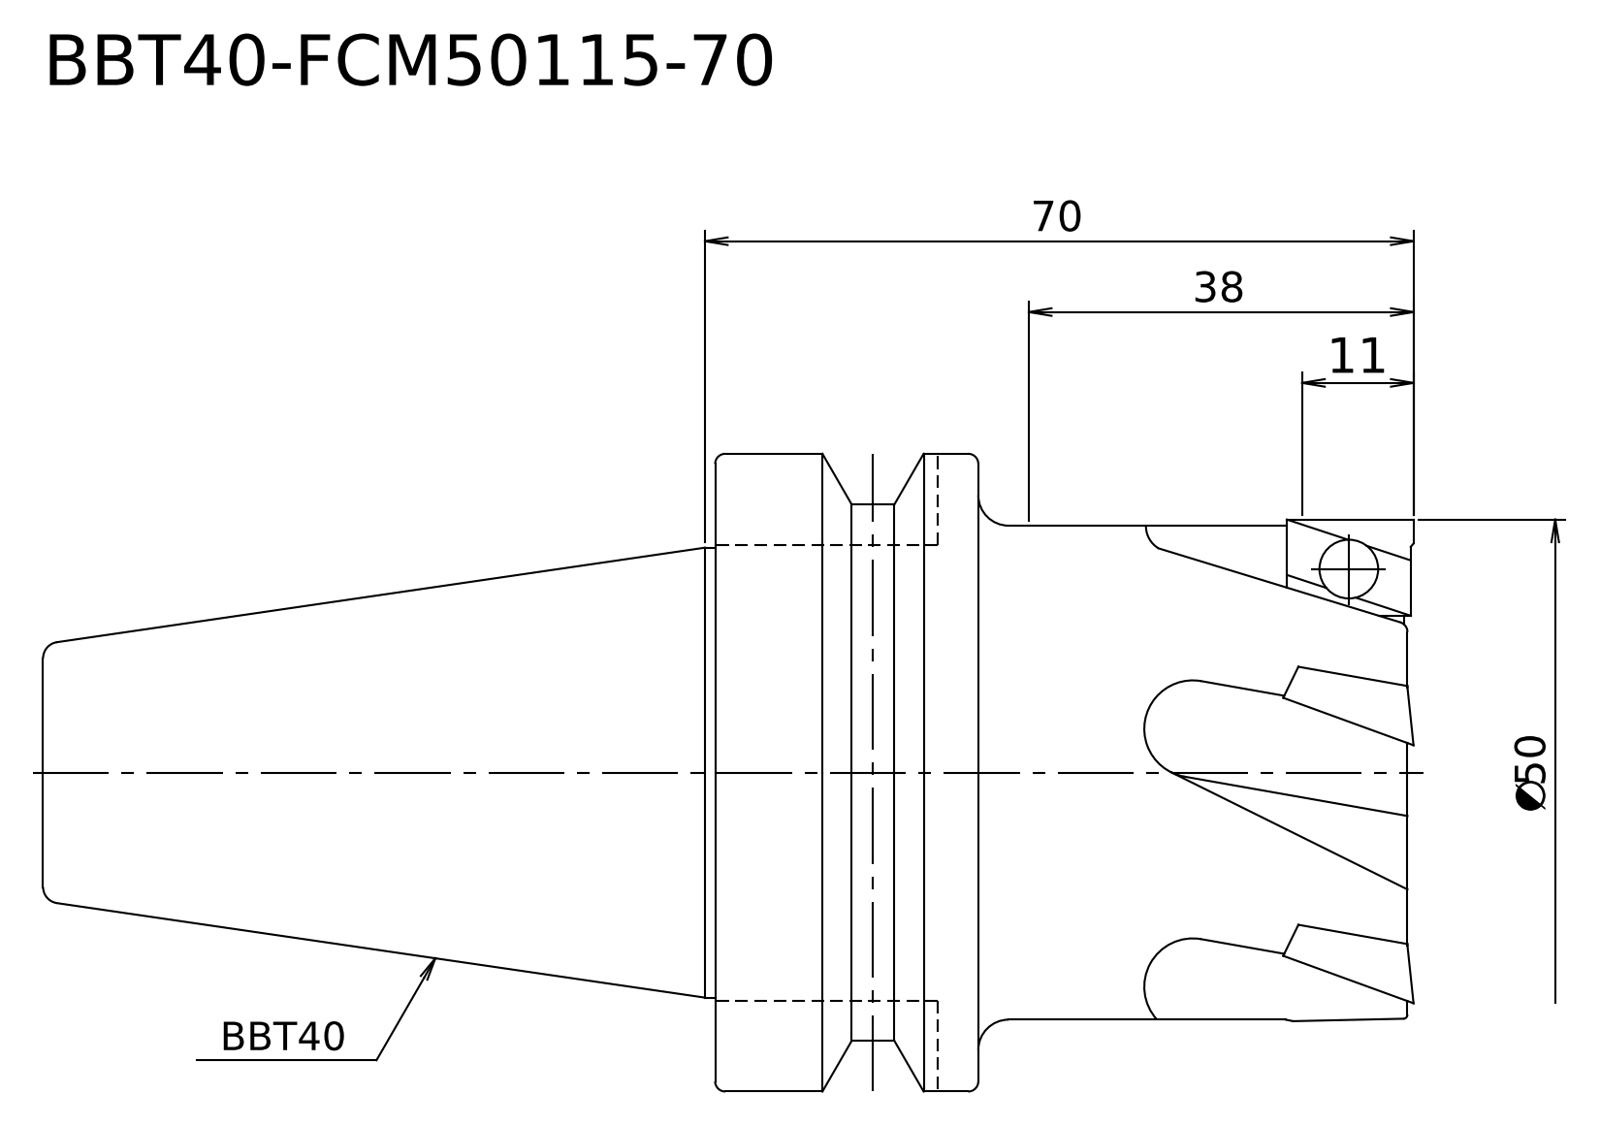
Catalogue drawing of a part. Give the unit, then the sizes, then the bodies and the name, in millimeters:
Units: millimetres
Overall size (bounding box): 135.4 × 63 × 63
Round bosses / shafts (diameter × count): ⌀63 ×1, ⌀53 ×1, ⌀50 ×1, ⌀48.8 ×1, ⌀44.45 ×1
Main face-to-face distances: 69, 43, 26, 135.4, 92.4, 66.4
Volume: 222 454 mm³ · Surface area: 25 040 mm²
Bodies: 1 solid, 15 faces (4 planar, 6 cylindrical, 5 other)
STEP written by: Kubotek KeyCreator V8.5.1 (14335) (CONFIG_CONTROL_DESIGN)
